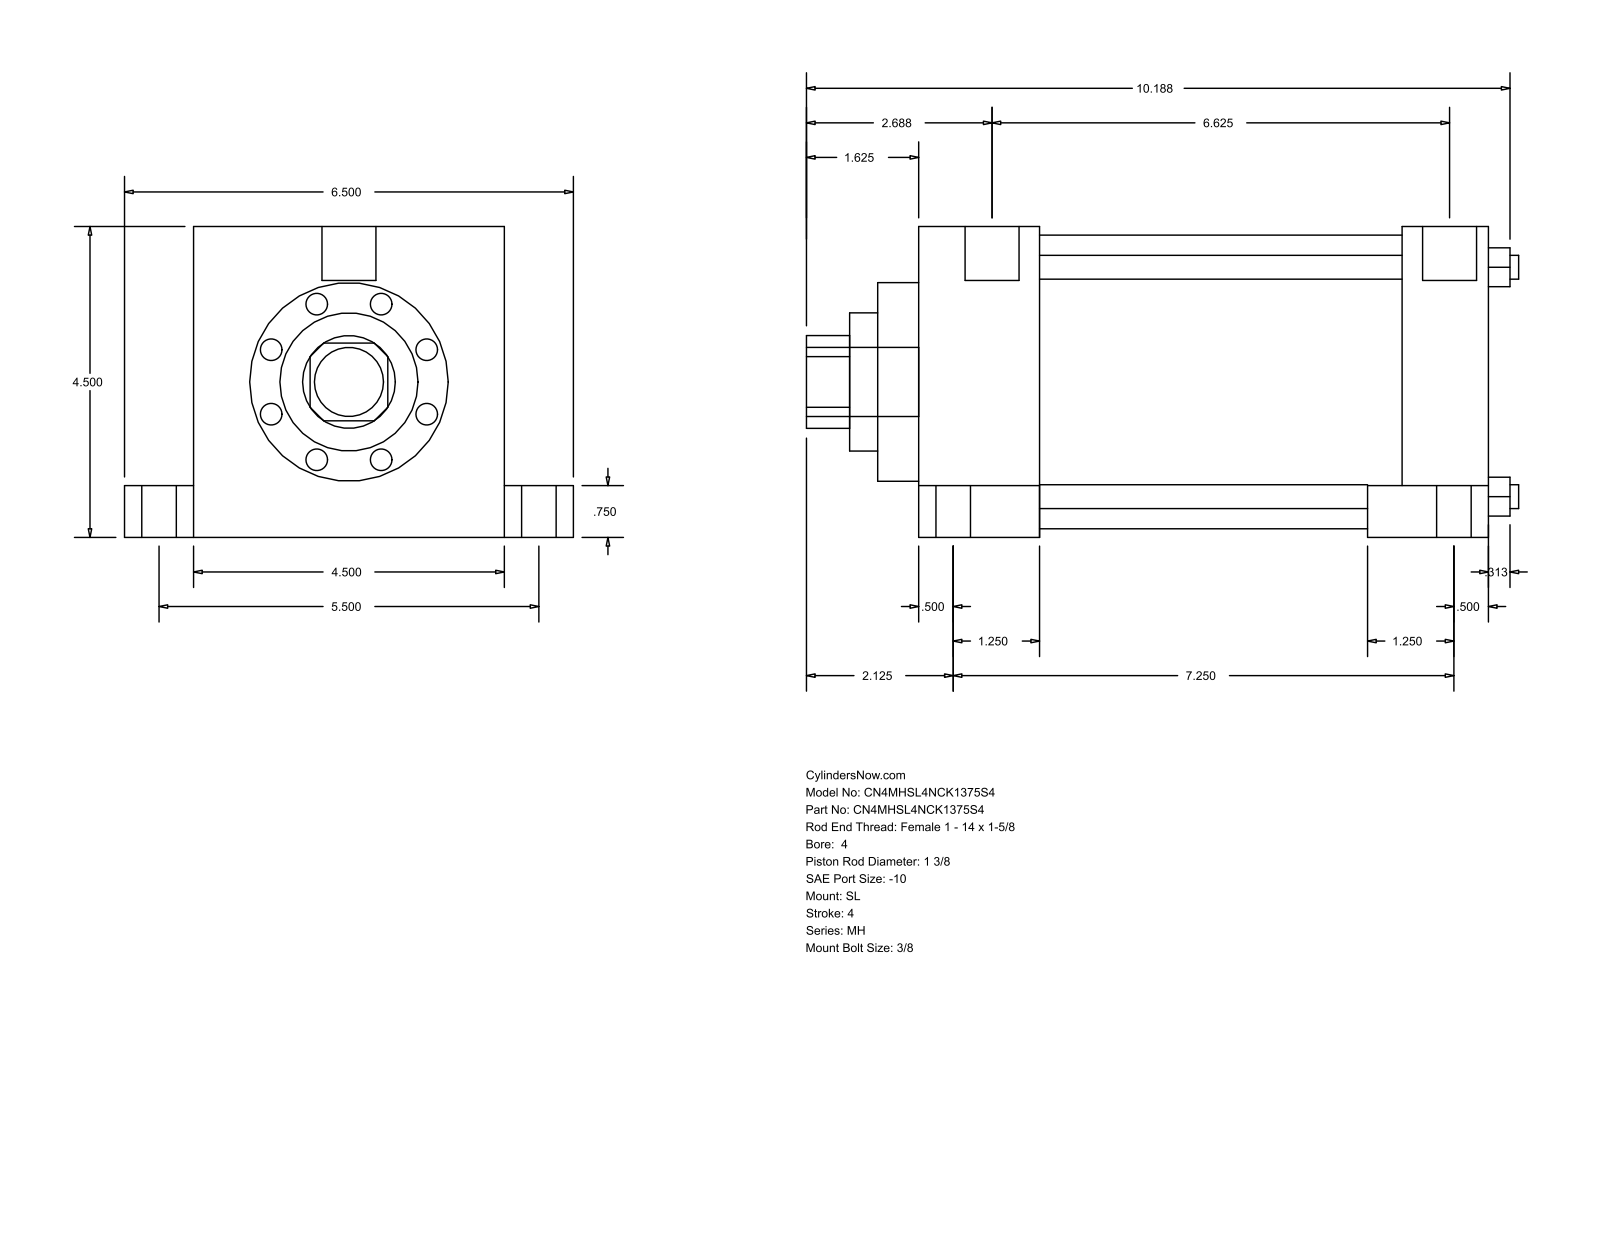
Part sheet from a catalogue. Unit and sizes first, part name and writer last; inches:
Units: inches
Overall size (bounding box): 10.313 × 6.5 × 4.5
Round holes (diameter × count): ⌀0.345 ×4, ⌀1.375 ×1, ⌀2 ×1, ⌀2.875 ×1, ⌀4.25 ×1
Round bosses / shafts (diameter × count): ⌀0.75 ×4, ⌀0.5 ×4, ⌀0.344 ×4, ⌀0.781 ×2, ⌀1 ×1
Partial cylindrical surfaces — rounded edges, fillets, slot ends (radius × count): R0.672 ×1
Main face-to-face distances: 4.5, 8.25, 6.5, 1.75, 7, 5.25, 1.25, 1, 5.5, 0.75
Hole centre spacings: 2.347, 3.32, 4.695
Bodies: 0 solids, 110 faces (77 planar, 33 cylindrical, 0 other)
Part name (STEP PRODUCT): MH_SL__0400_1.375
STEP written by: GSSL Pune (CONFIG_CONTROL_DESIGN)
